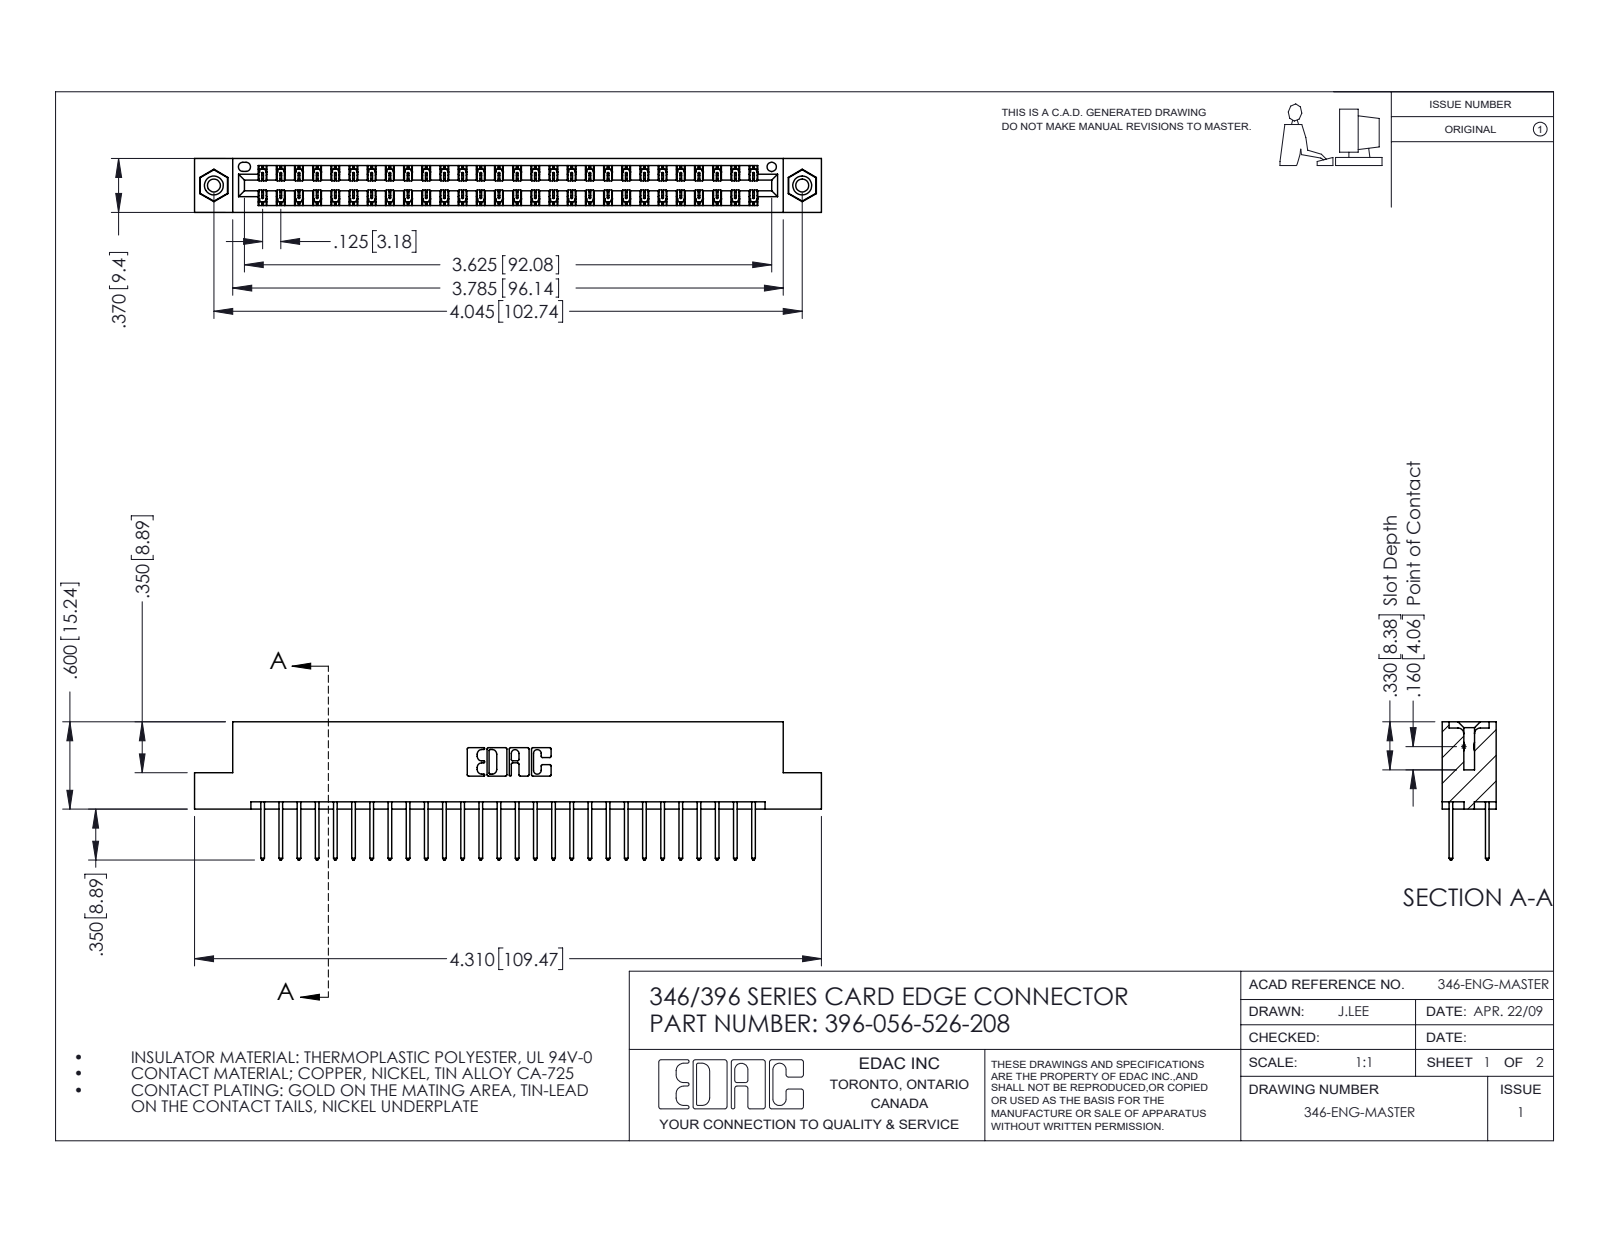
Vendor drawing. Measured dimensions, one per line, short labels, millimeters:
name: 345-250-001_345-250-003-102; 396-056-526-208; 345-292-001_345-293-126; 346 Part_Flush Mounting Lugs - 0.156 Dia-TI
written by: SolidWorks 2016 (CONFIG_CONTROL_DESIGN)
unit: mm
bodies: 59 solids, 3094 faces (2068 planar, 1010 cylindrical, 16 other)
size: 109.5 × 24.1 × 9.4
volume: 10 700 mm³; area: 14 850 mm²
holes: 2× ⌀2.3, 2× ⌀3.2, 2× ⌀4, 1× ⌀1.6
bosses: 2× ⌀3.9
rounds: 84× R0.2, 56× R0.3, 22× R0.3, 6× R0.2, 6× R0.8, 3× R0.7, 2× R0.4, 2× R0.6
face distances: 1.2, 8.2, 6.4, 9.4, 1.8, 7.6, 0.6, 7, 3.8, 5.6
hole spacings: 6.2, 97.5, 102.7
